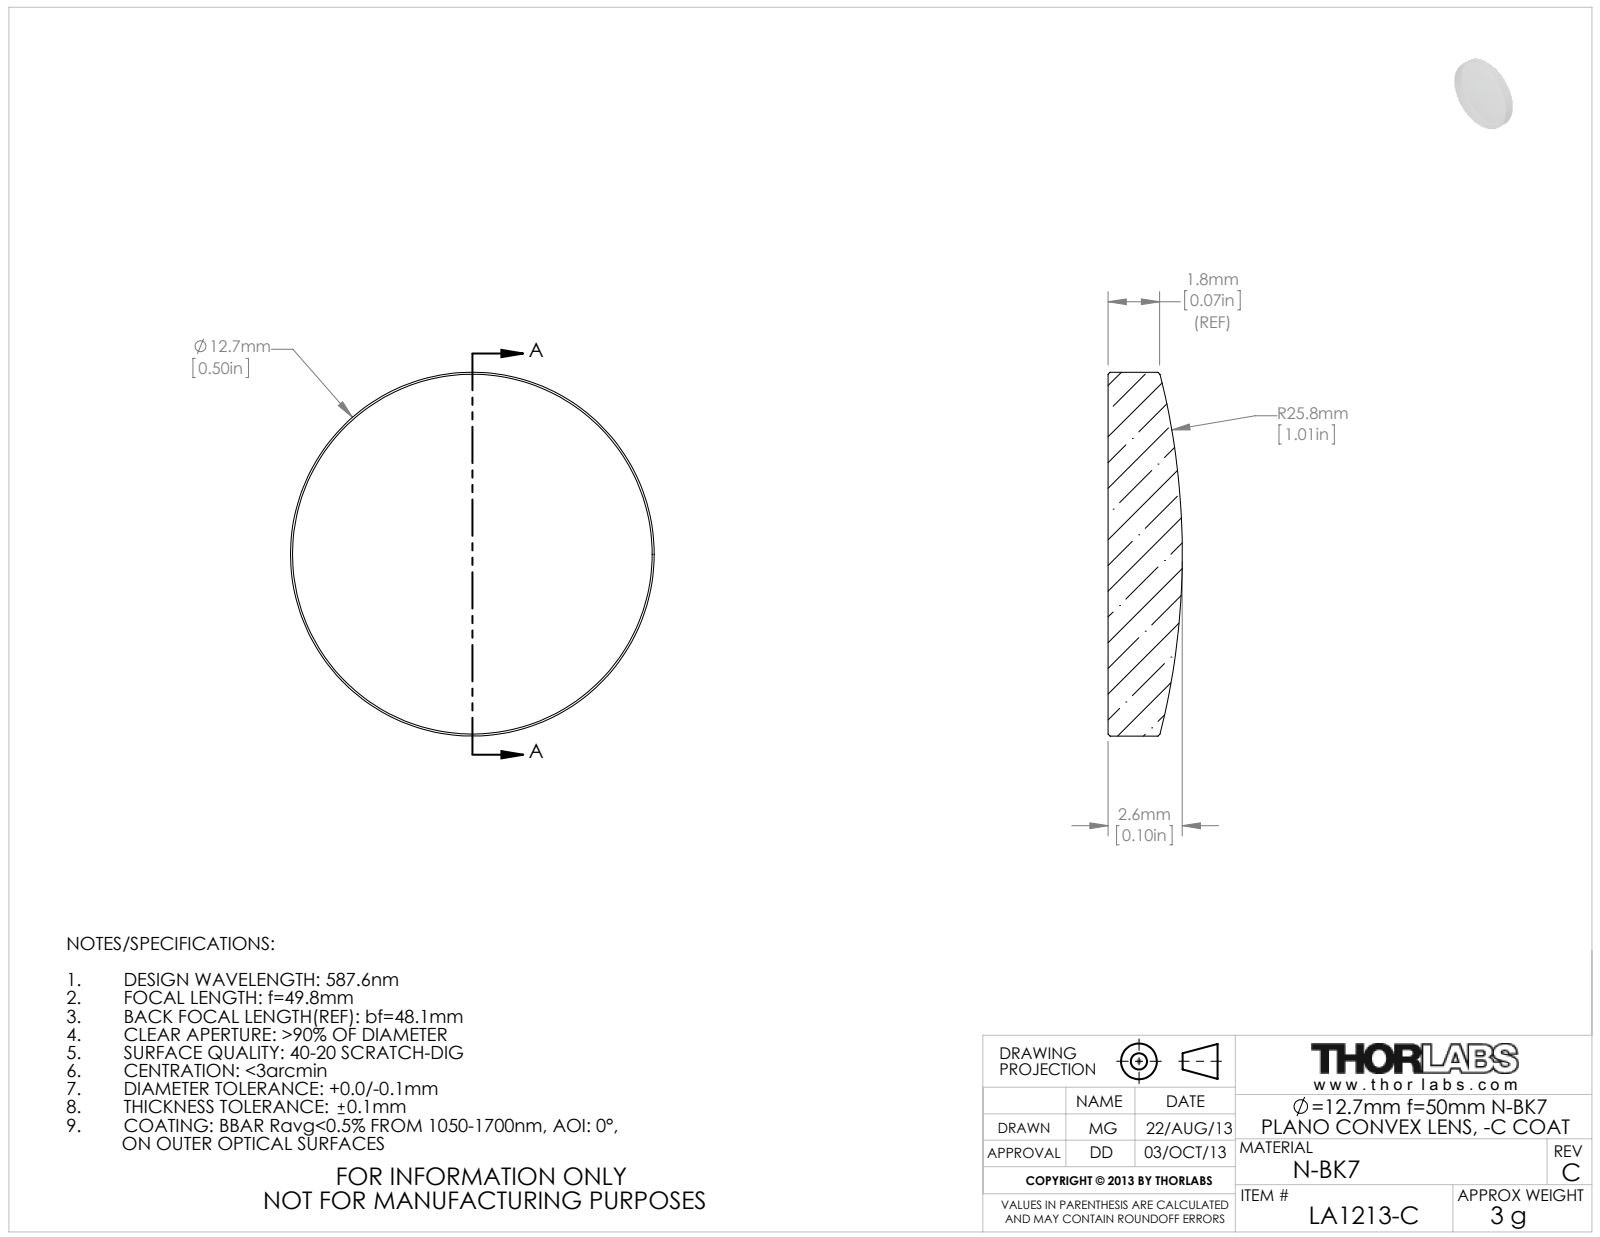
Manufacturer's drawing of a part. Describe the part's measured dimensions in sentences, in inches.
The part is named "4571-E0W". Its 3-D file was written by "SolidWorks 2009 (AUTOMOTIVE_DESIGN)". It is 1 solid with 5 faces: 1 planar, 2 cylindrical and 2 other. Overall it measures 0.5 by 0.5 by 0.102 inches. Its volume is 0.017 cubic inches and its surface area 0.507 square inches. Round bosses or shafts: 1 of diameter 0.5.
